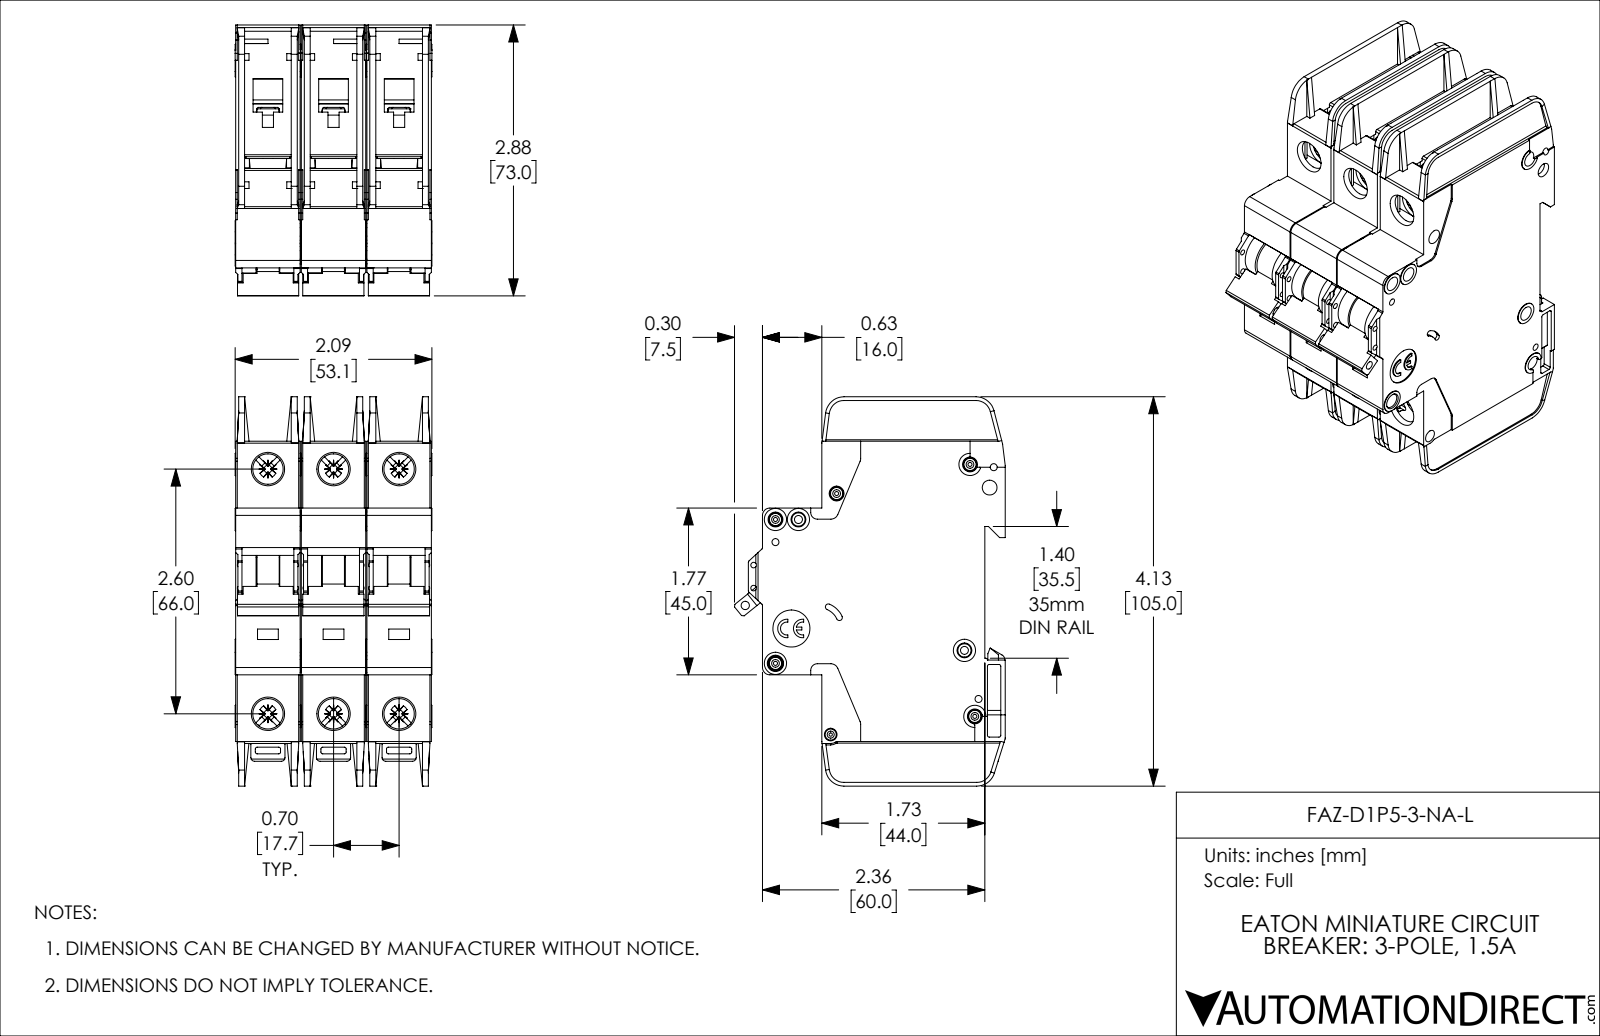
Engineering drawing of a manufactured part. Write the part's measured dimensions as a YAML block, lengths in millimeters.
part_name: "FAZ-D1P5-3-NA-L"
step_written_by: "SolidWorks 2019 (AUTOMOTIVE_DESIGN)"
units: millimeters
bodies: {solids: 3, faces: 3381, planar: 2013, cylindrical: 1071, other: 297}
overall_size: [105, 73.1, 53.1]
volume: 230200
surface_area: 79350
round_holes:
  - {diameter: 4, count: 8}
  - {diameter: 8.2, count: 6}
  - {diameter: 1.1, count: 5}
  - {diameter: 1.9, count: 4}
  - {diameter: 1.5, count: 2}
  - {diameter: 2.2, count: 2}
  - {diameter: 0.9, count: 1}
  - {diameter: 2.3, count: 1}
  - {diameter: 2.5, count: 1}
  - {diameter: 3.4, count: 1}
  - {diameter: 10, count: 1}
round_bosses_or_shafts:
  - {diameter: 3.3, count: 5}
  - {diameter: 6, count: 4}
  - {diameter: 3, count: 4}
  - {diameter: 2.5, count: 3}
partial_cylinders:
  - {radius: 0.5, count: 72}
  - {radius: 0.4, count: 30}
  - {radius: 1, count: 18}
  - {radius: 1.1, count: 12}
  - {radius: 2, count: 12}
  - {radius: 0.2, count: 6}
  - {radius: 0.3, count: 6}
  - {radius: 0.7, count: 6}
face_to_face_distances: [17.7, 1.2, 35.4, 17.4, 15, 35.1, 18.9, 16.5, 2.7, 2.4]
hole_center_spacings: [17.7, 68.3, 66, 6.2, 13.6, 22.1, 35.4, 74.9]
